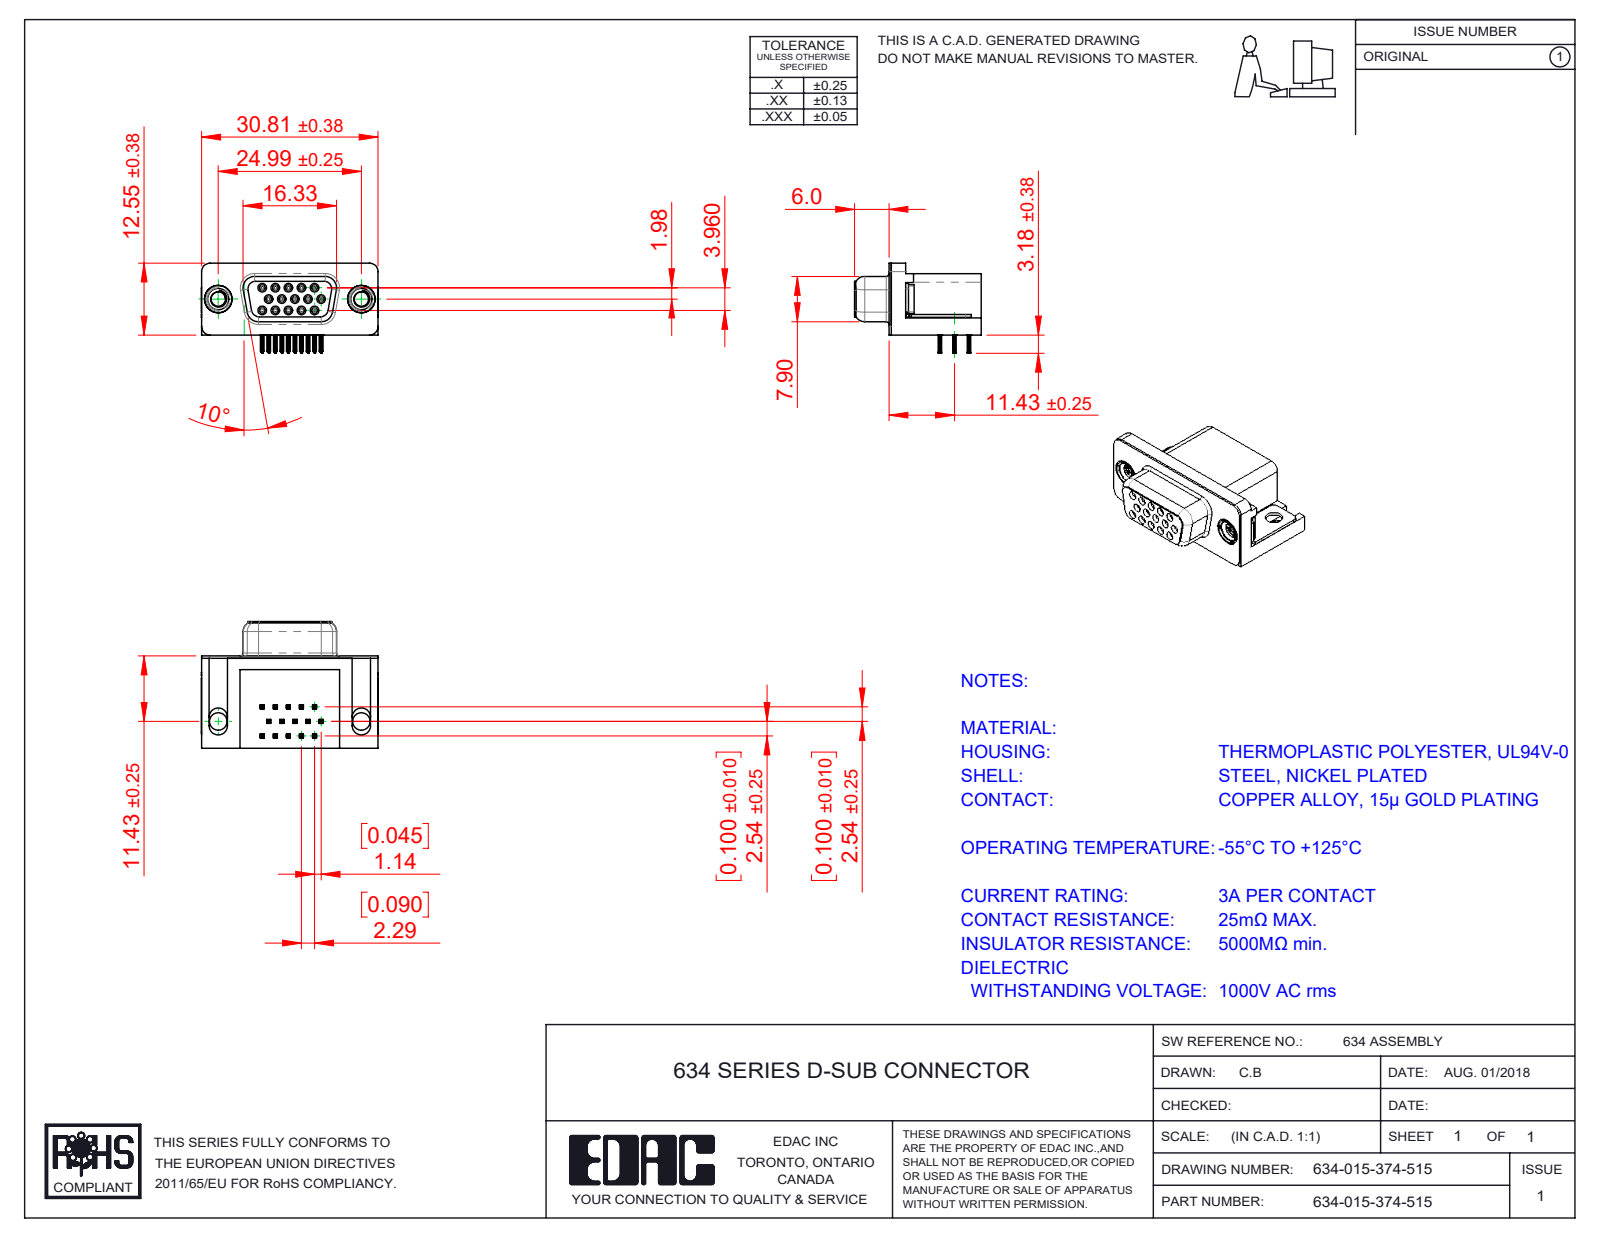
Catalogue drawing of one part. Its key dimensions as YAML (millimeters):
part_name: "634-015-374-515; Contact Middle; 634 Housing; M3 Threaded Rivet (+5 more)"
step_written_by: "SolidWorks 2016 (CONFIG_CONTROL_DESIGN)"
units: millimeters
bodies: {solids: 21, faces: 2419, planar: 1064, cylindrical: 603, other: 752}
overall_size: [30.89, 22.1, 15.73]
volume: 4546
surface_area: 6489
round_holes:
  - {diameter: 0.8, count: 15}
  - {diameter: 0.9, count: 15}
  - {diameter: 2.5, count: 2}
  - {diameter: 3.05, count: 2}
  - {diameter: 4, count: 2}
  - {diameter: 4.8, count: 2}
  - {diameter: 5, count: 2}
round_bosses_or_shafts:
  - {diameter: 1.2, count: 15}
  - {diameter: 4.9, count: 2}
  - {diameter: 4.75, count: 2}
  - {diameter: 3.9, count: 2}
partial_cylinders:
  - {radius: 0.1, count: 120}
  - {radius: 0.15, count: 60}
  - {radius: 0.35, count: 30}
  - {radius: 1, count: 19}
  - {radius: 0.34, count: 15}
  - {radius: 0.25, count: 8}
  - {radius: 1.35, count: 8}
  - {radius: 1.6, count: 8}
face_to_face_distances: [0.4, 10.35, 15.7, 16.1, 0.35, 0.6, 2.5, 2.9, 0.5, 6.4]
hole_center_spacings: [2.29, 2.28, 3.96, 4.57, 6.05, 3.97, 4.58, 6.86]
